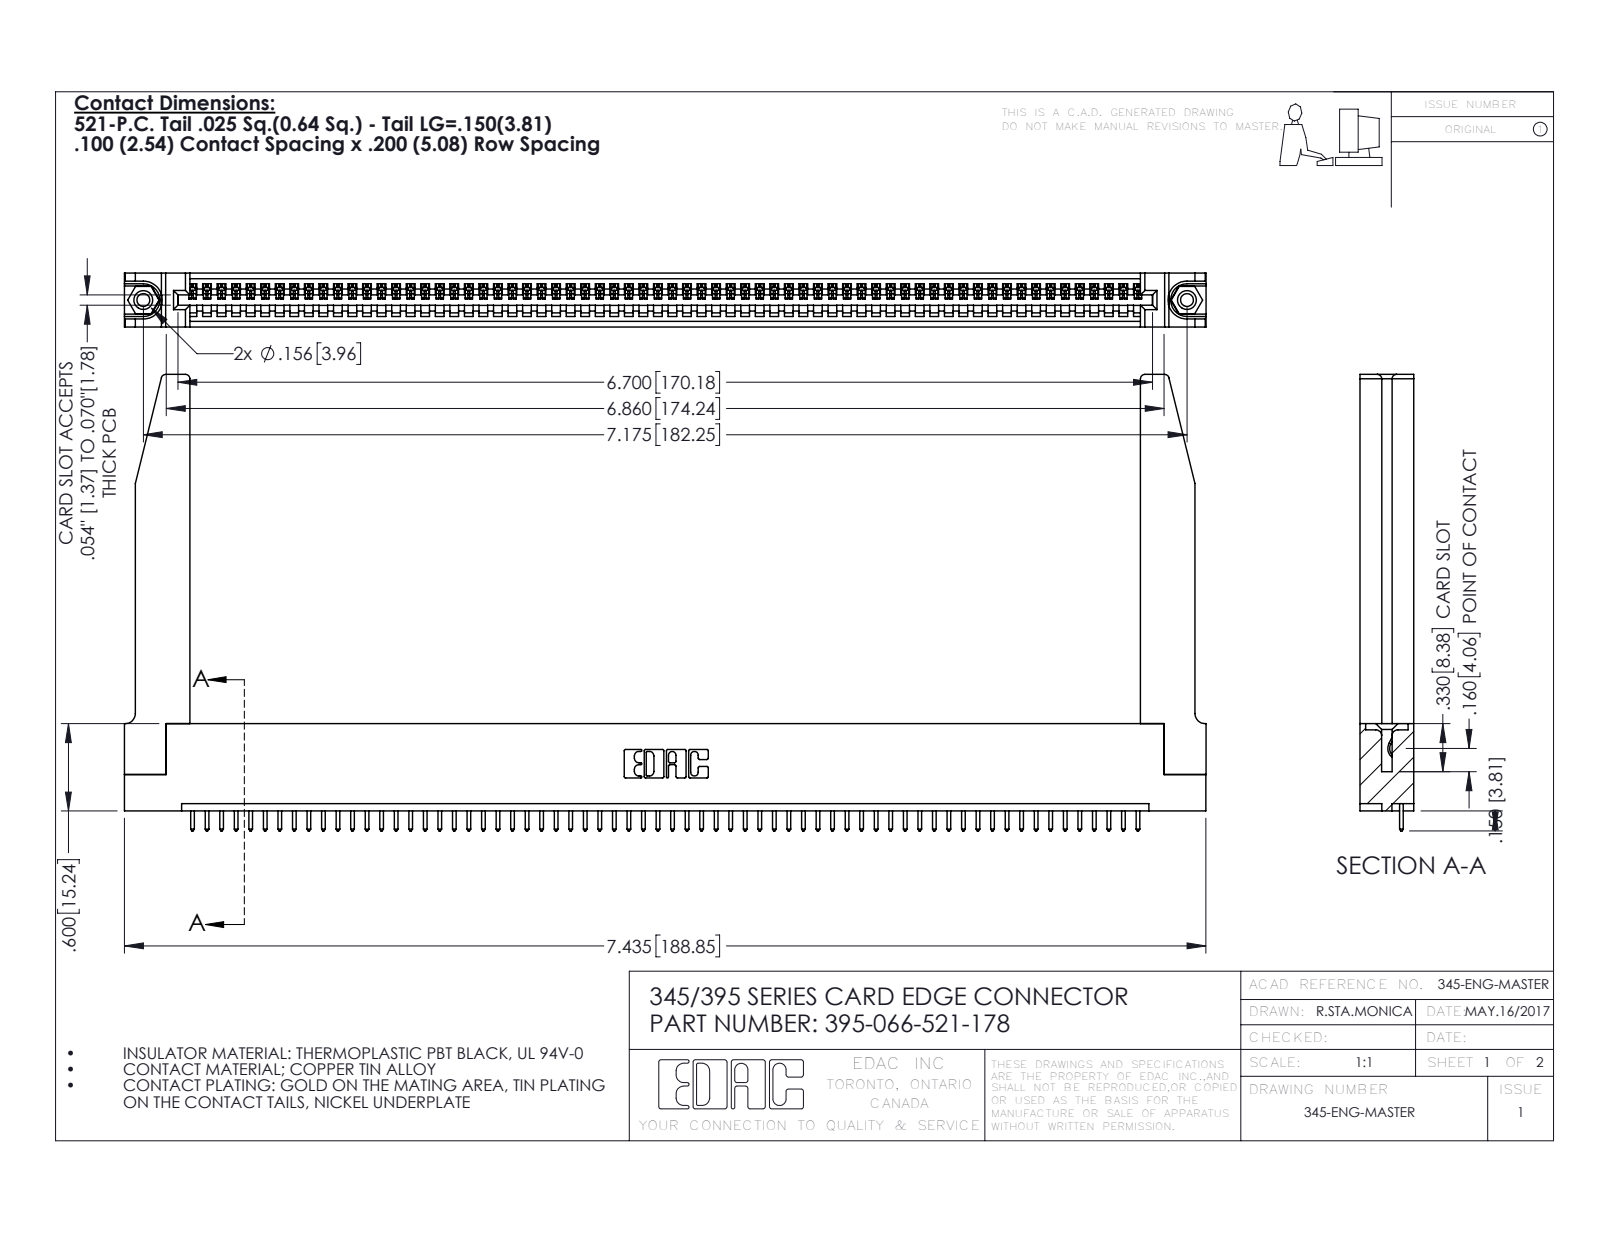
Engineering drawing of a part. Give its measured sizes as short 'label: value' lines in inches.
name: 395-066-521-178; 345-250-001_345-250-001-102; 345 Part_Flush Mounting Lugs - 0.156 Dia-TH; 345-220-078_345-220-078 (+1 more)
written by: SolidWorks 2016 (CONFIG_CONTROL_DESIGN)
unit: in
bodies: 71 solids, 4188 faces (2862 planar, 1274 cylindrical, 52 other)
size: 7.436 × 3.137 × 0.37
volume: 1.569 in³; area: 46.95 in²
holes: 2× ⌀0.089, 2× ⌀0.125, 2× ⌀0.156, 1× ⌀0.064
bosses: 2× ⌀0.155
rounds: 132× R0.006, 132× R0.01, 22× R0.01, 8× R0.03, 6× R0.007, 6× R0.031, 3× R0.026, 2× R0.031
face distances: 0.072, 0.37, 0.298, 0.2, 0.098, 0.272, 0.025, 0.225, 0.149, 0.15
hole spacings: 0.27, 6.939, 7.175
